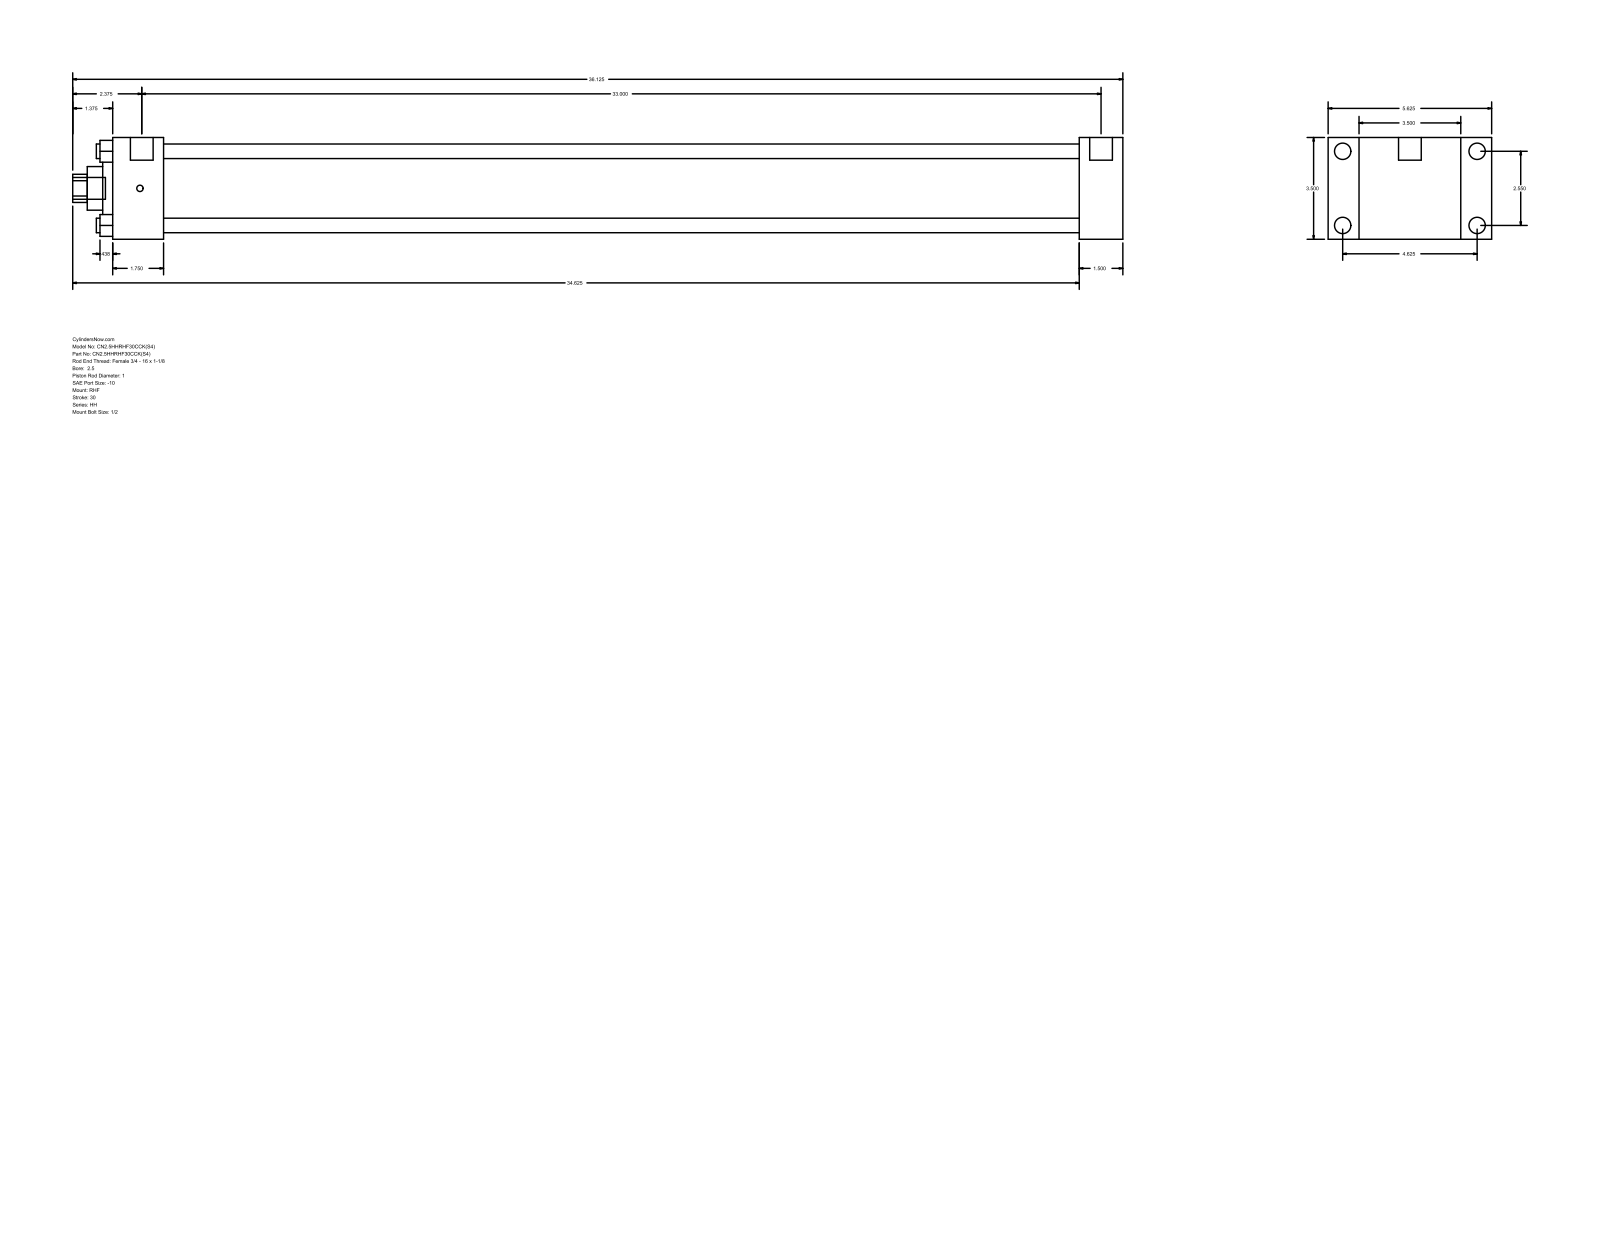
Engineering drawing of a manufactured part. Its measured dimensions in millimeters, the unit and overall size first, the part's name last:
Units: millimetres
Overall size (bounding box): 917.58 × 142.88 × 88.9
Round holes (diameter × count): ⌀12.7 ×4, ⌀25.4 ×1, ⌀38.1 ×1, ⌀60.33 ×1, ⌀73.03 ×1
Round bosses / shafts (diameter × count): ⌀14.3 ×4, ⌀5.56 ×4, ⌀19.84 ×2, ⌀19.05 ×1
Partial cylindrical surfaces — rounded edges, fillets, slot ends (radius × count): R12.29 ×1
Main face-to-face distances: 88.9, 38.1, 26.99, 115.89, 844.56, 882.66, 142.88, 44.46, 800.1, 838.2
Hole centre spacings: 45.79, 64.76, 91.58
Bodies: 0 solids, 90 faces (61 planar, 29 cylindrical, 0 other)
Part name (STEP PRODUCT): HH_RHF__0250_1
STEP written by: GSSL Pune (CONFIG_CONTROL_DESIGN)
